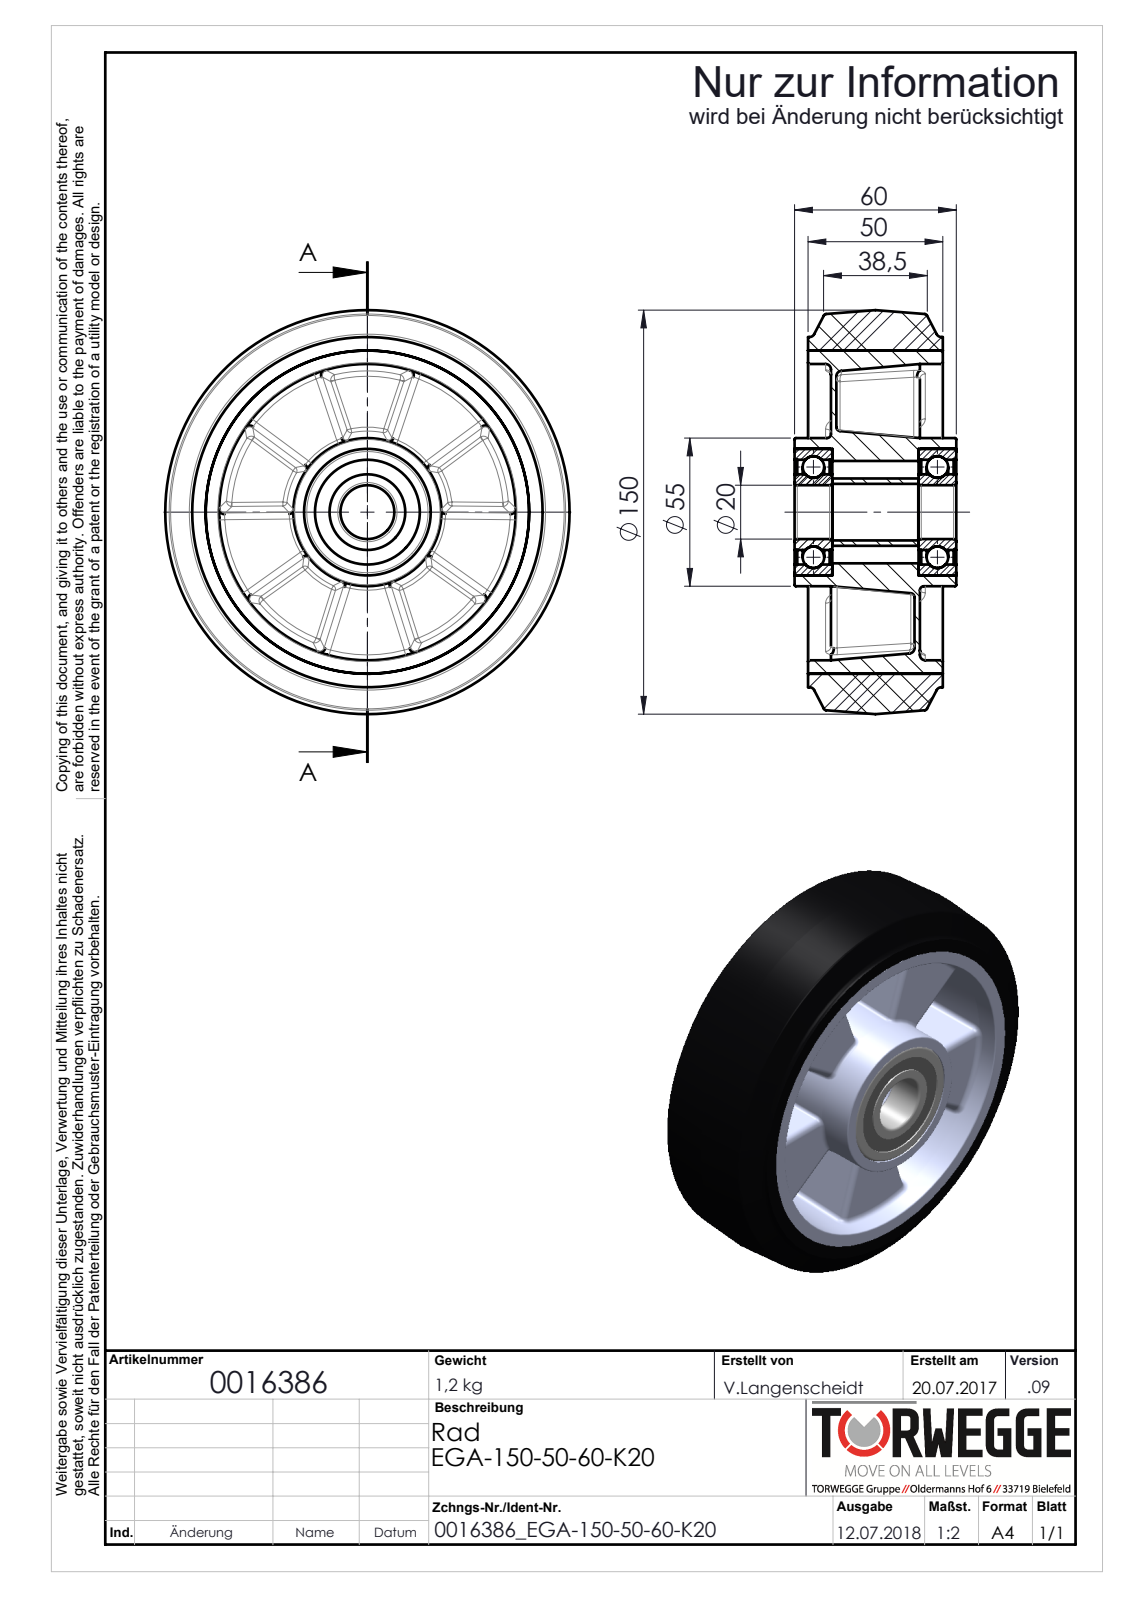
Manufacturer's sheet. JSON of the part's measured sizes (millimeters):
{"part_name": "K0016386_EGA-150-50-60-K20", "step_written_by": "SolidWorks 2016 (AUTOMOTIVE_DESIGN)", "units": "millimeters", "bodies": {"solids": 0, "faces": 299, "planar": 44, "cylindrical": 54, "other": 201}, "overall_size": [150, 150, 60], "round_holes": [[20, 1], [21, 1], [38.9, 1], [47, 1], [110, 1], [120, 1]], "round_bosses_or_shafts": [[130, 1], [55, 1], [28.1, 1]], "partial_cylinders_radius": [[2.5, 20]], "face_to_face_distances": [8.5, 41.5, 50, 2.87, 13.5, 33, 5, 46.5, 55, 0.5]}
